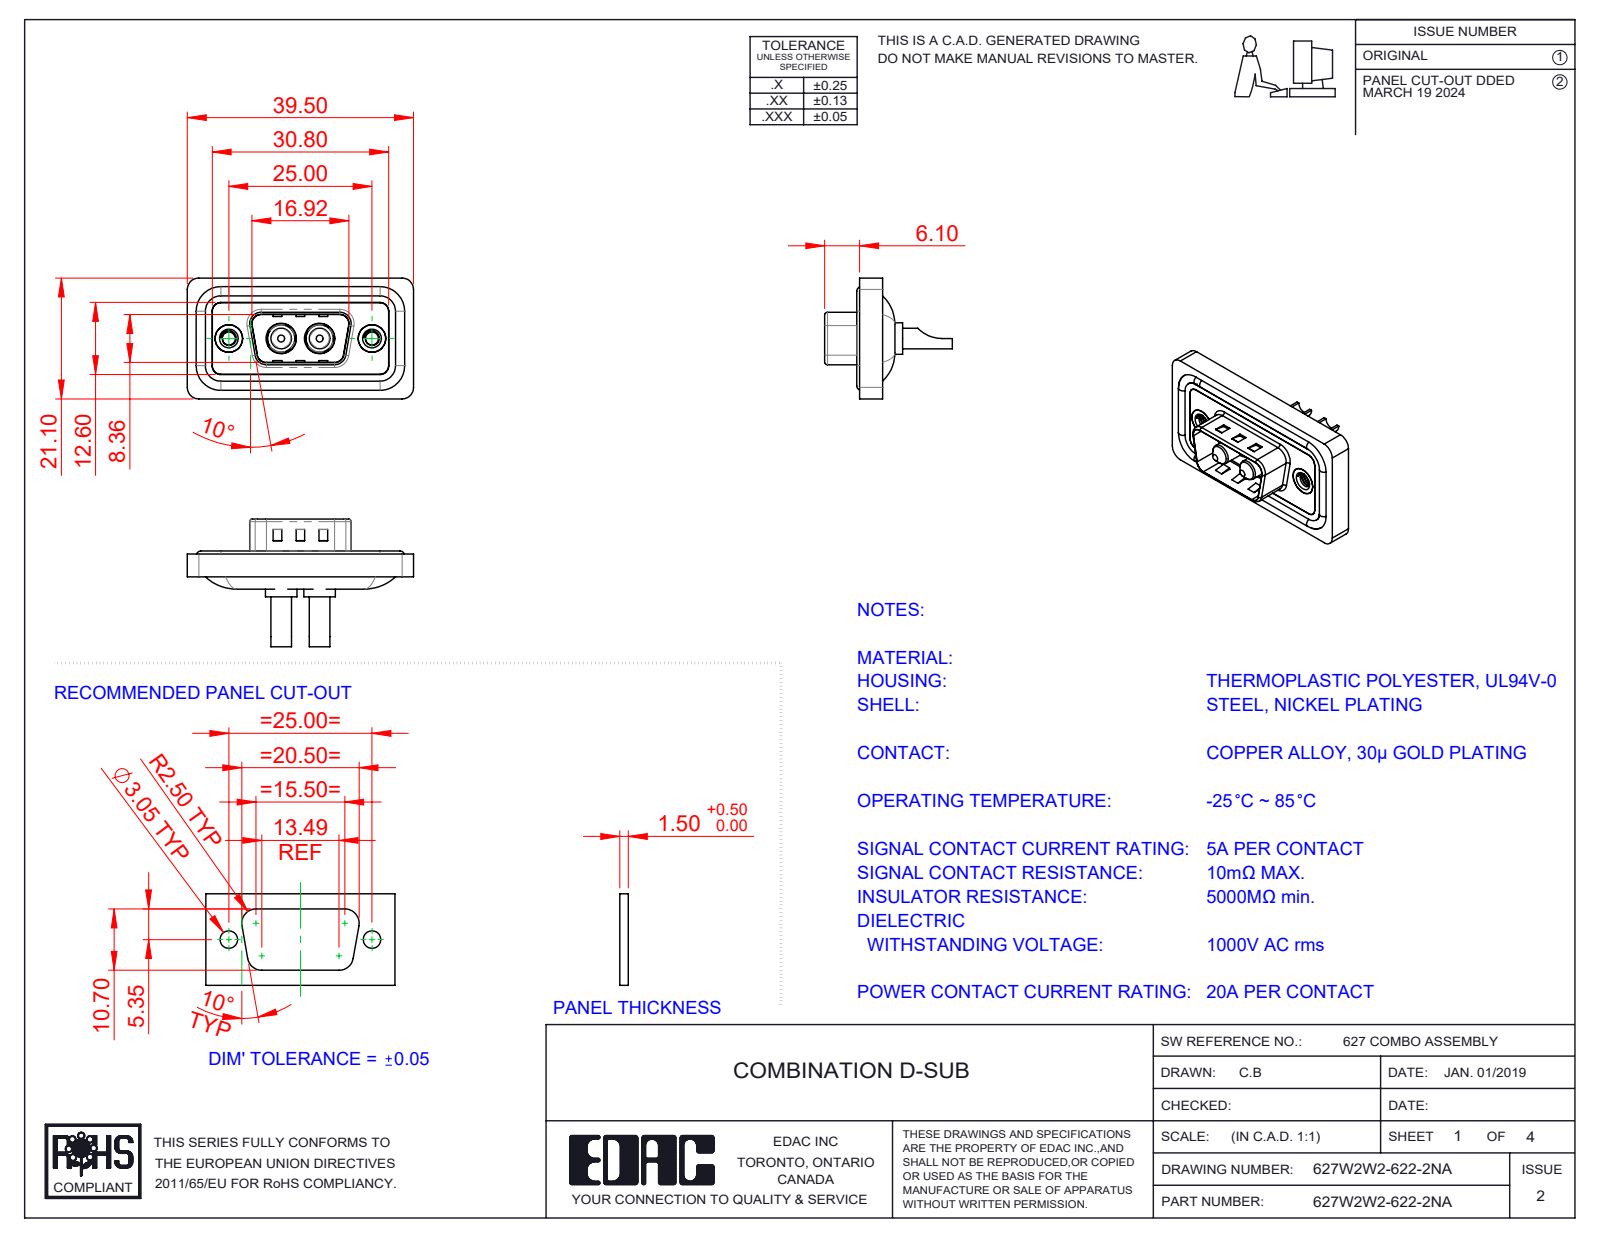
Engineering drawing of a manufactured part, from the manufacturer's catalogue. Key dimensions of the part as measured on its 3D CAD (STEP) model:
Part name (STEP PRODUCT): 627Combo Threaded Rivet_A; 627Combo Shell Front_09 Contacts; 627Combo Housing_2W2; 627Combo Waterproof Housing_09 Contacts (+3 more)
STEP written by: SolidWorks 2023 (CONFIG_CONTROL_DESIGN)
Units: millimetres
Bodies: 11 solids, 501 faces (171 planar, 226 cylindrical, 104 other)
Overall size (bounding box): 39.5 × 22.3 × 21.1
Volume: 4 488 mm³ · Surface area: 7 146 mm²
Round holes (diameter × count): ⌀2.26 ×2, ⌀2.7 ×2, ⌀4 ×2, ⌀4.8 ×2, ⌀4.85 ×2, ⌀5 ×2, ⌀5.3 ×2
Round bosses / shafts (diameter × count): ⌀1.6 ×4, ⌀5.5 ×2, ⌀5.2 ×2, ⌀4.9 ×2, ⌀4.75 ×2, ⌀3.75 ×2, ⌀3.6 ×2
Partial cylindrical surfaces — rounded edges, fillets, slot ends (radius × count): R1.5 ×22, R2 ×18, R0.5 ×8, R1.6 ×8, R0.25 ×4, R0.6 ×4, R0.65 ×4, R0.9 ×4
Main face-to-face distances: 0.4, 1.1, 2.9, 3.1, 0.5, 1.6, 1.5, 4, 2.5, 0.7
Hole centre spacings: 9.14, 15.86, 6.72, 25
